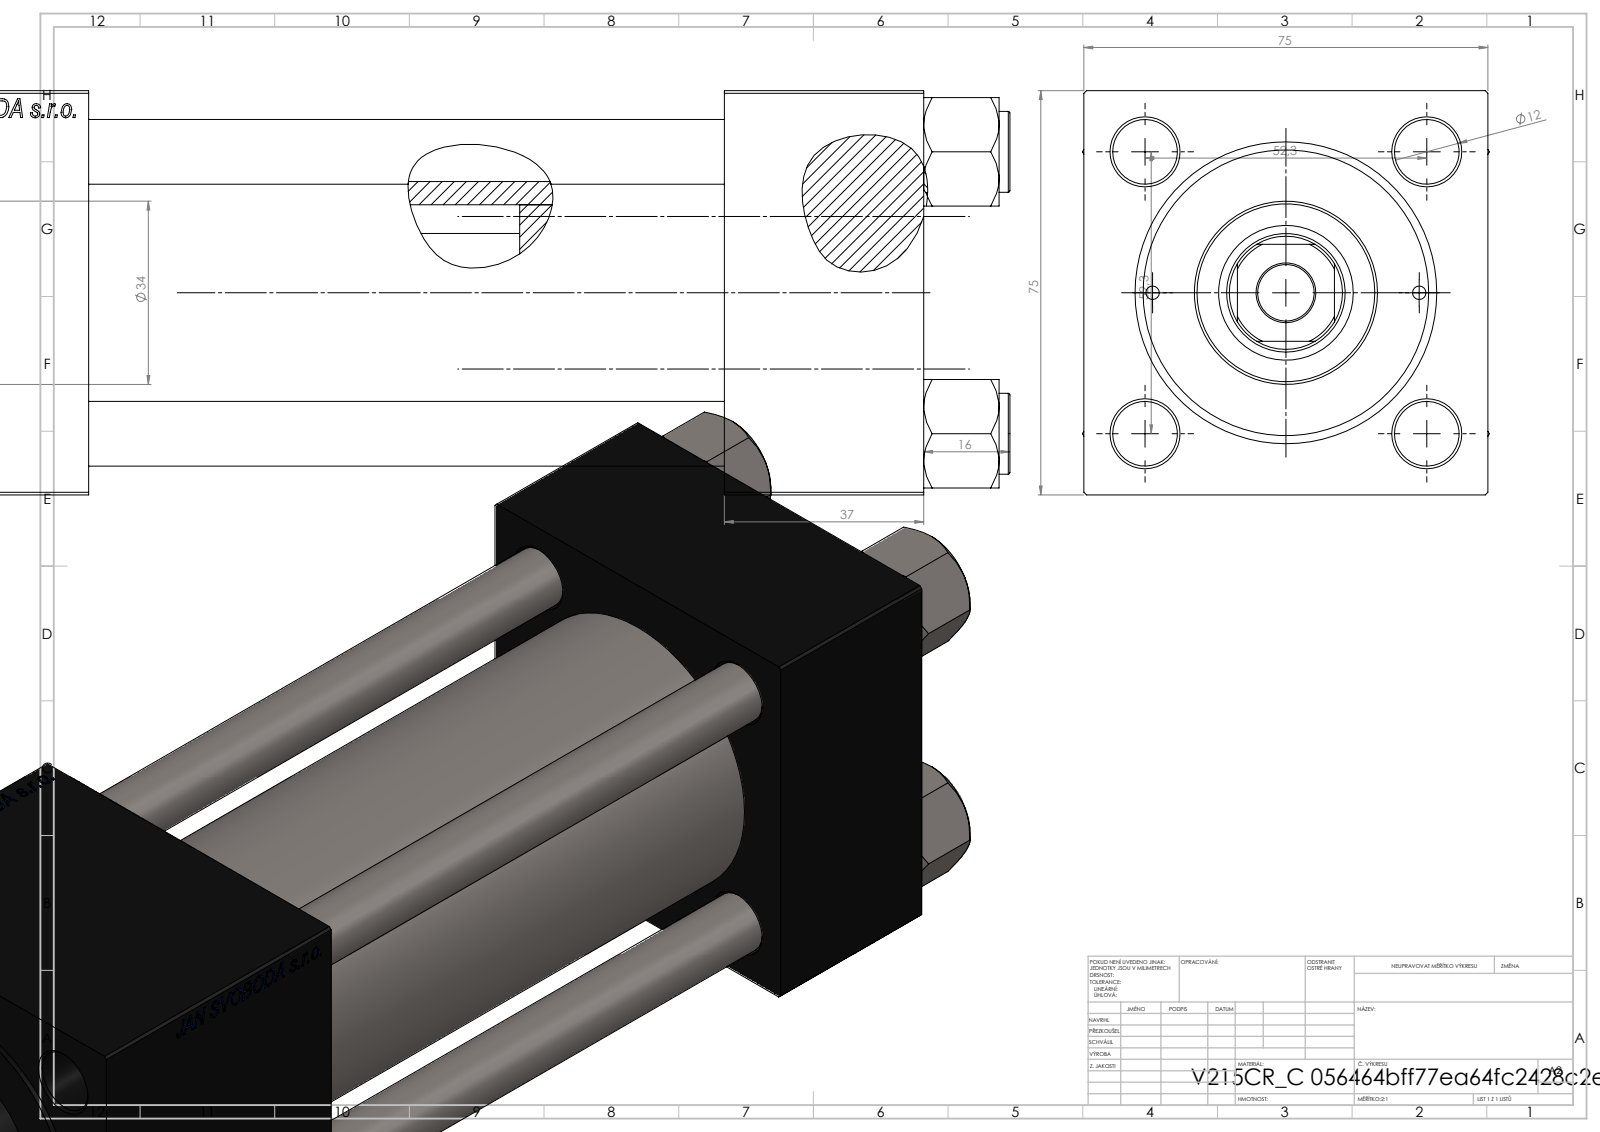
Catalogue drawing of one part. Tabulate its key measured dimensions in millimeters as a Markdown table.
| quantity | value |
| --- | --- |
| part name | V215CR_VCP_C; NUT_M5_C; V215_VC_A; V215CR_C_Body (+1 more) |
| STEP written by | SolidWorks 2019 (CONFIG_CONTROL_DESIGN) |
| units | millimeters |
| bodies | 11 solids, 1155 faces (528 planar, 91 cylindrical, 536 other) |
| overall size | 255 × 75.54 × 75 |
| volume | 736 745 mm³ |
| surface area | 180 540 mm² |
| round holes (diameter × count) | 12 × 4, 2.5 × 2, 7 × 2, 20.96 × 2, 30 × 2, 10.5 × 1, 22 × 1, 25 × 1, 41 × 1, 50 × 1, 53 × 1 |
| round bosses / shafts (diameter × count) | 15 × 4, 56 × 1, 34 × 1 |
| partial cylindrical surfaces (radius × count) | 10.5 × 1 |
| main face-to-face distances | 75, 37, 214, 177, 155, 118, 59, 185.3, 148.3, 30.3 |
| hole center spacings | 26.19, 36.98, 52.3, 57.22, 24.75, 73.96, 49.5, 153.5 |
